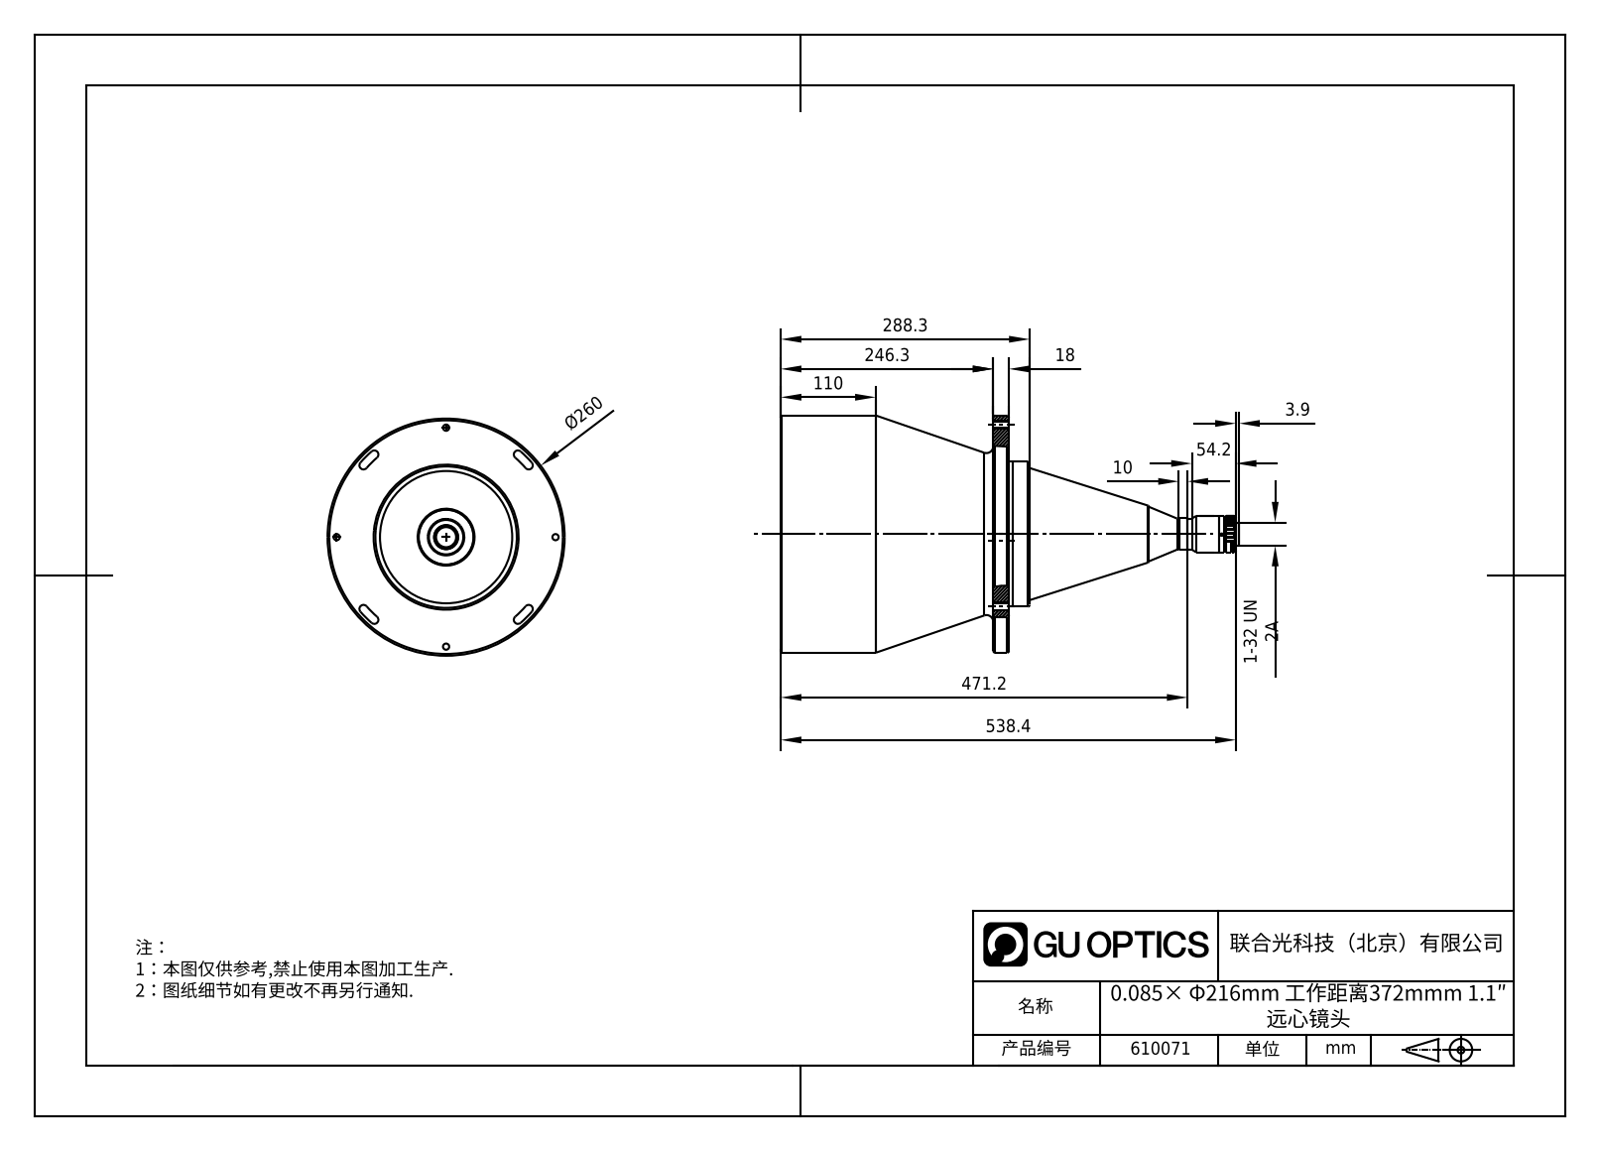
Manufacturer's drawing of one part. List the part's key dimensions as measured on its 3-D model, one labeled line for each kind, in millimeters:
Part name (STEP PRODUCT): DTCM111-216-AL
STEP written by: SolidWorks 2017 (CONFIG_CONTROL_DESIGN)
Units: millimetres
Bodies: 1 solid, 100 faces (8 planar, 54 cylindrical, 38 other)
Overall size (bounding box): 542.3 × 260 × 260
Volume: 13 670 000 mm³ · Surface area: 396 593 mm²
Round holes (diameter × count): ⌀6.8 ×4, ⌀2.5 ×3
Round bosses / shafts (diameter × count): ⌀260 ×1, ⌀159 ×1, ⌀40 ×1, ⌀35 ×1, ⌀34 ×1, ⌀29 ×1, ⌀25.4 ×1
Partial cylindrical surfaces — rounded edges, fillets, slot ends (radius × count): R4.5 ×8, R115.5 ×1, R124.5 ×1
Main face-to-face distances: 264.3, 246.3, 18, 288.3, 42, 24, 520, 273.7, 255.7, 231.7
Hole centre spacings: 169.71, 240
